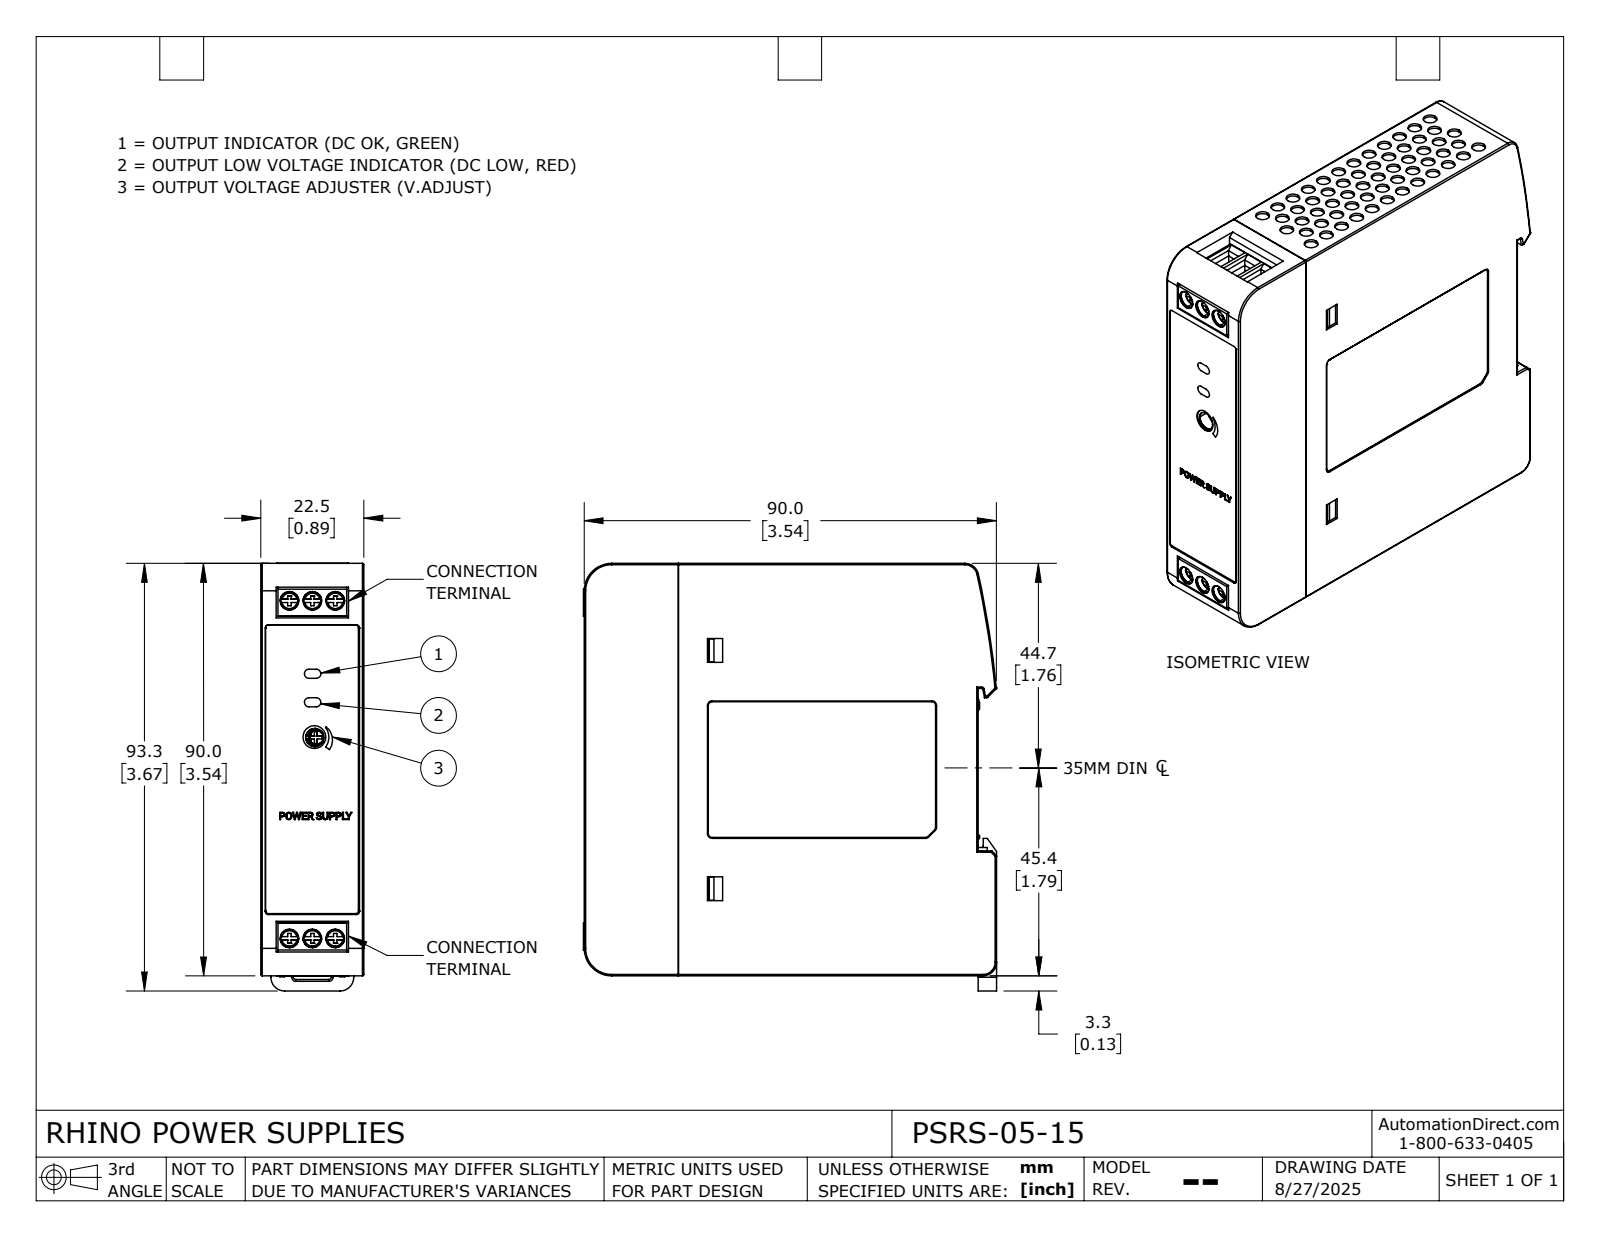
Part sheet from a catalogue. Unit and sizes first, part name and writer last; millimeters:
Units: millimetres
Overall size (bounding box): 93.3 × 90.17 × 22.5
Round holes (diameter × count): ⌀3.82 ×6, ⌀4.05 ×6, ⌀4 ×3, ⌀3.4 ×1
Round bosses / shafts (diameter × count): ⌀3.95 ×6, ⌀3 ×1, ⌀2 ×1
Partial cylindrical surfaces — rounded edges, fillets, slot ends (radius × count): R0.3 ×48, R1 ×11, R0.1 ×8, R3 ×8, R0.5 ×7, R2.5 ×3, R0.6 ×2, R1.1 ×2
Main face-to-face distances: 22.5, 22.35, 90, 85.85, 0.5, 89.5, 4, 2, 89.85, 15.3
Hole centre spacings: 5, 73.79, 73.62, 10, 29.82, 74.3, 6.2, 7.61
Volume: 174 150 mm³ · Surface area: 28 728 mm²
Bodies: 1 solid, 1156 faces (635 planar, 183 cylindrical, 338 other)
Part name (STEP PRODUCT): SPB-A015-05
STEP written by: SolidWorks 2024 (AUTOMOTIVE_DESIGN)
